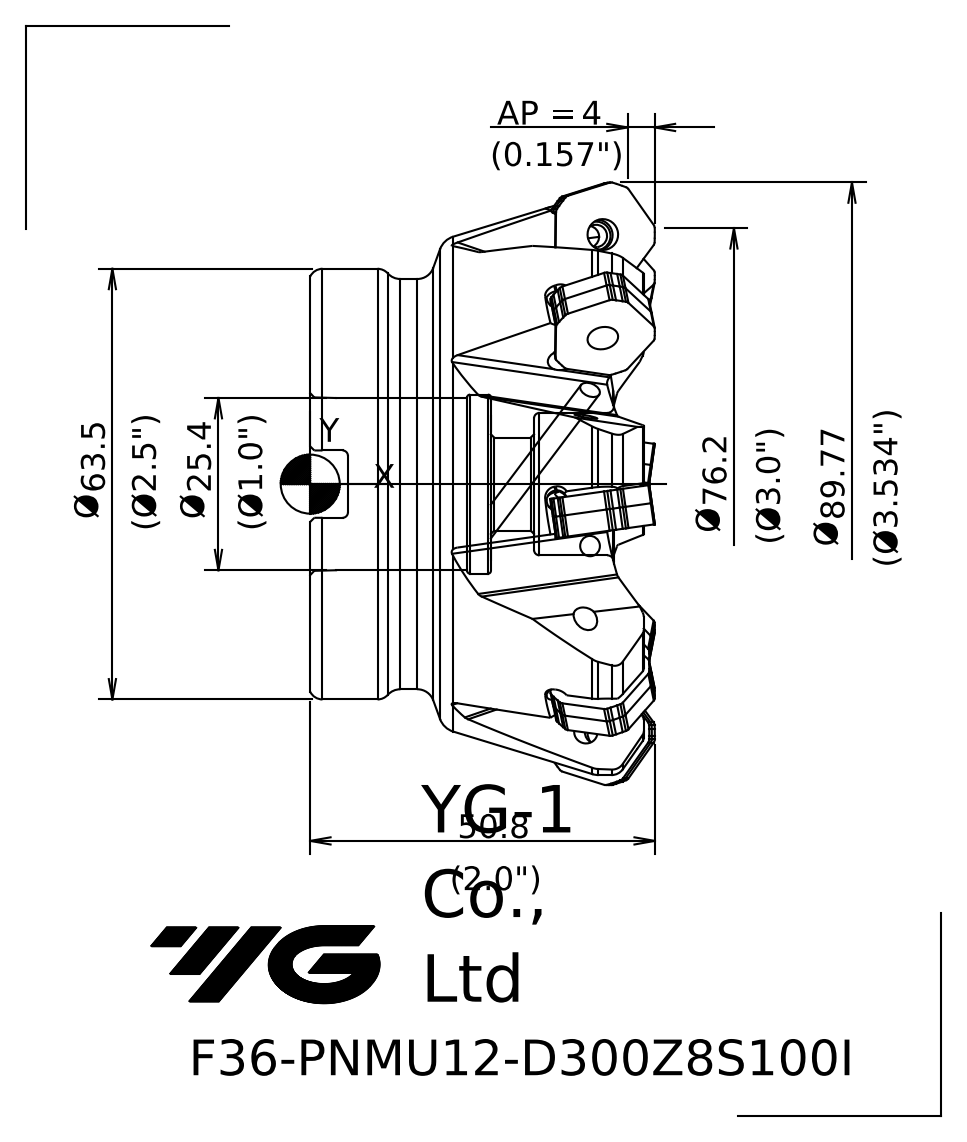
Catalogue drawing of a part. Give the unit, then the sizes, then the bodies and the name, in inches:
Units: inches
Overall size (bounding box): 3.534 × 3.534 × 2
Round holes (diameter × count): ⌀0.539 ×1, ⌀0.827 ×1, ⌀1 ×1, ⌀1.039 ×1
Round bosses / shafts (diameter × count): ⌀2.5 ×1, ⌀2.382 ×1
Partial cylindrical surfaces — rounded edges, fillets, slot ends (radius × count): R0.031 ×2
Main face-to-face distances: 1.77, 0.343, 1.426, 0.721, 0.378, 1.049, 1.551, 1.207, 0.83, 0.219
Volume: 11.39 in³ · Surface area: 39.17 in²
Bodies: 1 solid, 66 faces (17 planar, 10 cylindrical, 39 other)
Part name (STEP PRODUCT): 120185C07CB1h7zq
STEP written by: SIEMENS PLM Software NX 10.0 (AP203_CONFIGURATION_CONTROLLED_3D_DESIGN_OF_MECHANICAL_PARTS_AND_ASSEMBLIES_MIM_LF)
